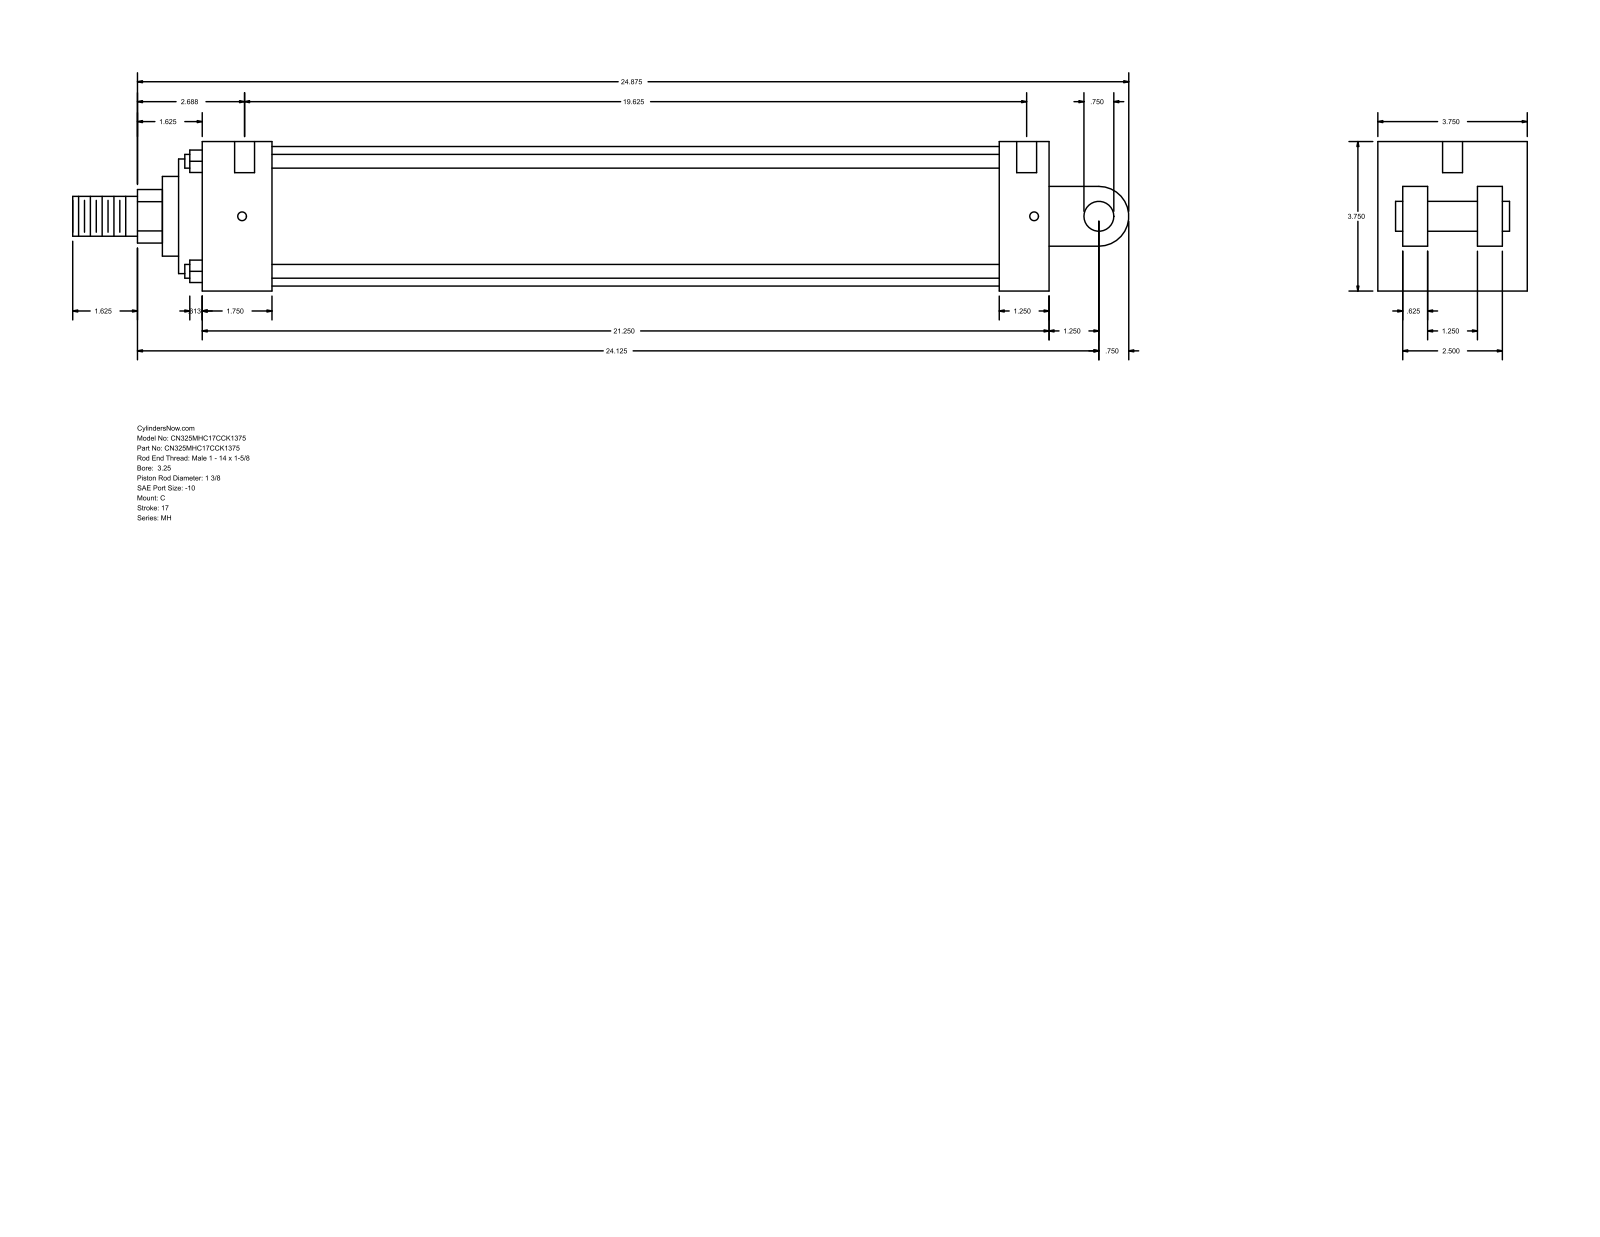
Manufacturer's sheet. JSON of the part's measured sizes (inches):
{"part_name": "MH_C__0325_1.375", "step_written_by": "GSSL Pune (CONFIG_CONTROL_DESIGN)", "units": "inches", "bodies": {"solids": 0, "faces": 101, "planar": 71, "cylindrical": 30, "other": 0}, "overall_size": [26.5, 3.75, 3.75], "round_holes": [[0.219, 4], [0.5, 2]], "round_bosses_or_shafts": [[0.345, 4], [3.5, 1], [2.875, 1], [2, 1], [1.375, 1], [1, 1], [0.75, 1]], "partial_cylinders_radius": [[0.672, 1], [0.75, 1]], "face_to_face_distances": [3.75, 0.625, 2.5, 21.25, 1.25, 3.125, 1.875, 1.75, 20, 18.25], "hole_center_spacings": [19.875, 0.063, 0.187, 19.625, 19.688, 19.813]}
